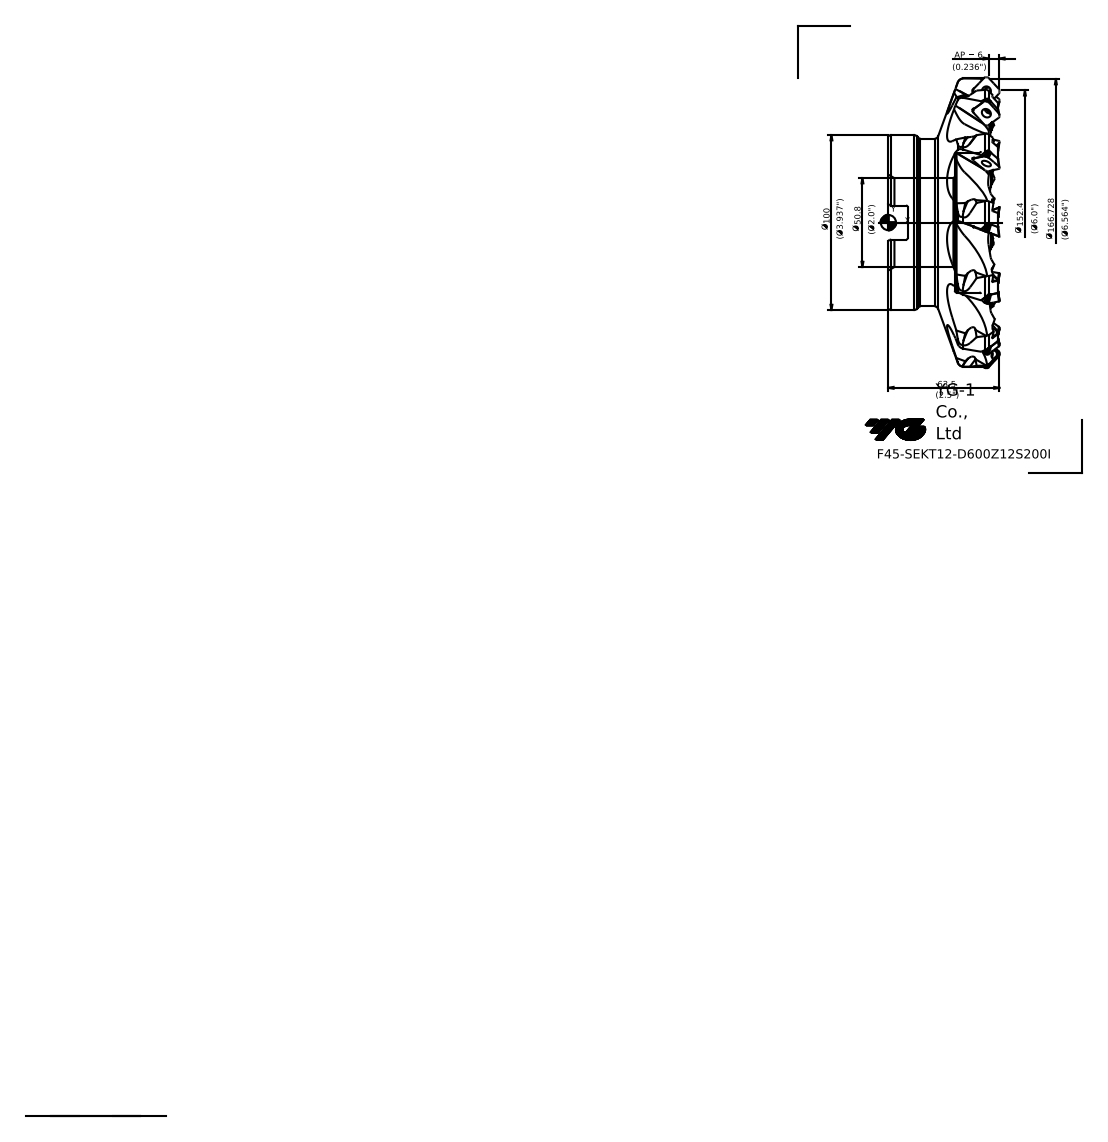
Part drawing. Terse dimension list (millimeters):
name: 102240C41AE7cq6i
written by: SIEMENS PLM Software NX 10.0 (AP203_CONFIGURATION_CONTROLLED_3D_DESIGN_OF_MECHANICAL_PARTS_AND_ASSEMBLIES_MIM_LF)
unit: mm
bodies: 1 solid, 63 faces (13 planar, 9 cylindrical, 41 other)
size: 166.73 × 166.73 × 63.5
volume: 561 898 mm³; area: 90 075 mm²
holes: 1× ⌀50.8, 1× ⌀80.01
bosses: 1× ⌀164.86, 1× ⌀100, 1× ⌀96
rounds: 2× R0.8
face distances: 38, 27, 11, 19.45
